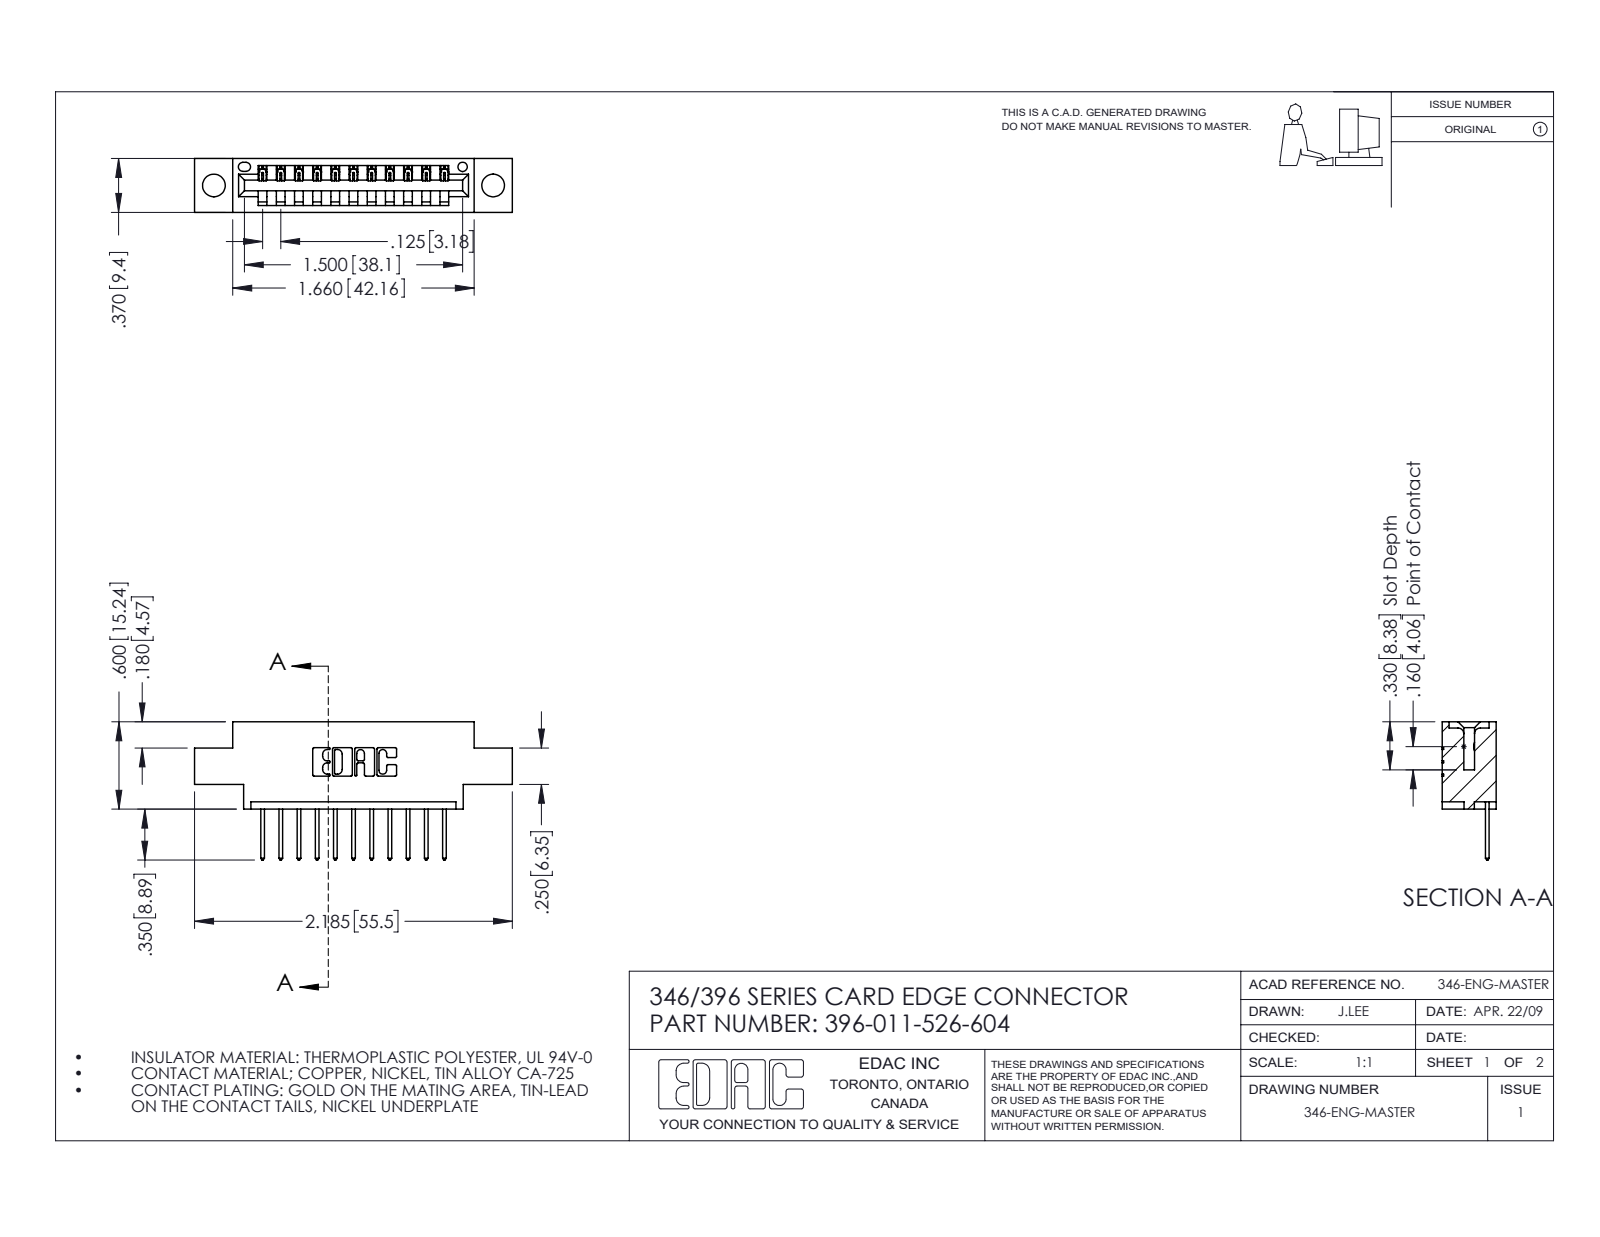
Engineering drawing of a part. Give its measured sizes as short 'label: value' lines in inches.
name: 346 Part_0.170 Offset - 0.156 Dia-TH; 345-292-001_345-293-126; 396-011-526-604
written by: SolidWorks 2016 (CONFIG_CONTROL_DESIGN)
unit: in
bodies: 12 solids, 764 faces (520 planar, 244 cylindrical, 0 other)
size: 2.185 × 0.95 × 0.37
volume: 0.296 in³; area: 8.803 in²
holes: 2× ⌀0.156, 1× ⌀0.064
rounds: 22× R0.006, 22× R0.01, 22× R0.01, 6× R0.007, 6× R0.031, 3× R0.026, 2× R0.031, 2× R0.04
face distances: 0.25, 0.37, 0.048, 0.322, 0.072, 0.298, 0.025, 0.148, 0.222, 0.1
hole spacings: 0.246, 1.715, 1.92
